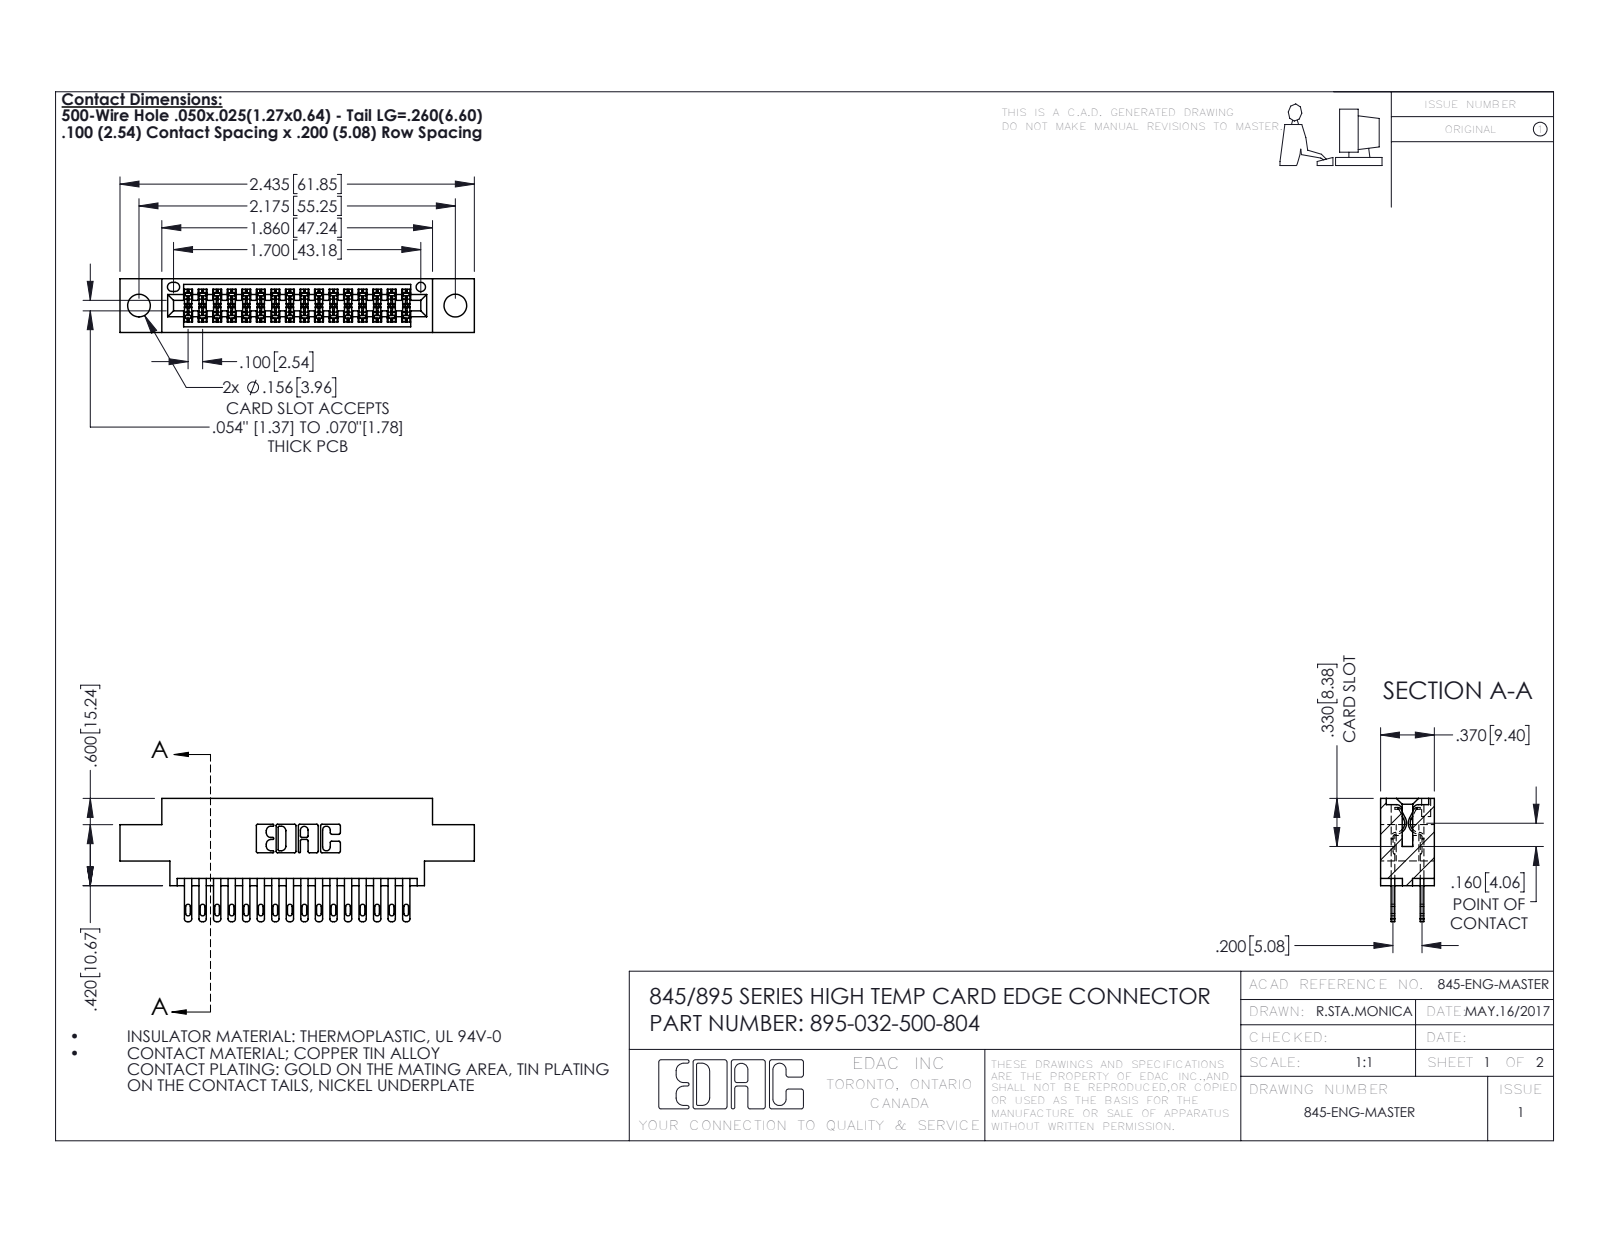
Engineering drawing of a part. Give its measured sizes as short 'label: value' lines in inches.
name: 845 Part_0.170 Offset - 0.156 Dia-TH; 895-032-500-804; 345-292-001_345-293-100
written by: SolidWorks 2020 (CONFIG_CONTROL_DESIGN)
unit: in
bodies: 33 solids, 1602 faces (948 planar, 654 cylindrical, 0 other)
size: 2.435 × 0.847 × 0.37
volume: 0.346 in³; area: 12.64 in²
holes: 2× ⌀0.156, 1× ⌀0.064
rounds: 48× R0.006, 32× R0.016, 32× R0.02, 22× R0.01, 6× R0.007, 6× R0.031, 3× R0.026, 2× R0.014
face distances: 0.072, 0.298, 0.2, 0.37, 0.098, 0.272, 0.025, 0.225, 0.175, 0.1
hole spacings: 0.27, 1.942, 2.175
